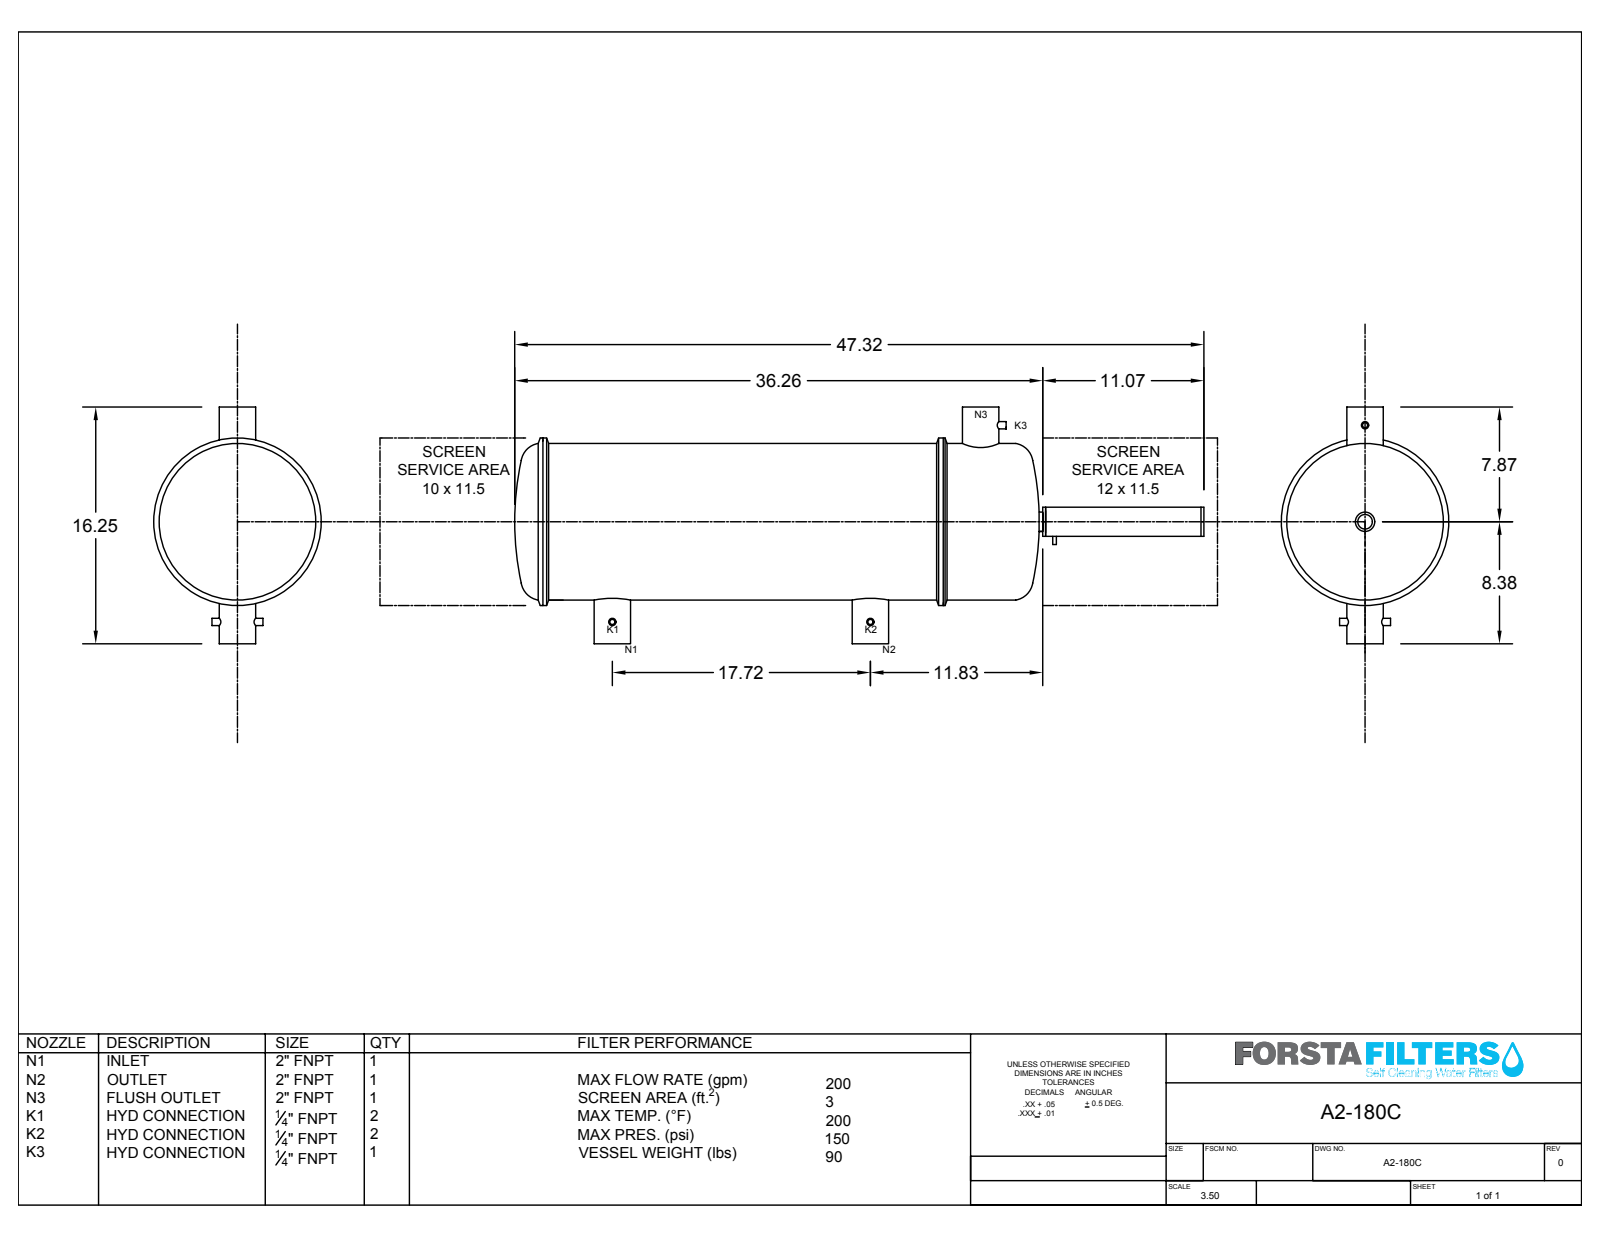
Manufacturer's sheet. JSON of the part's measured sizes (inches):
{"part_name": "A2-180C", "step_written_by": "SolidWorks 2017 (CONFIG_CONTROL_DESIGN)", "units": "inches", "bodies": {"solids": 6, "faces": 141, "planar": 39, "cylindrical": 58, "other": 44}, "overall_size": [47.324, 16.25, 11.493], "volume_in3": 311, "surface_area_in2": 2969, "round_holes": [[0.25, 3], [2, 3], [1, 2], [0.093, 1], [0.936, 1], [10.35, 1]], "round_bosses_or_shafts": [[2.394, 3], [0.644, 3], [11.493, 1], [10.743, 1], [1.993, 1], [0.25, 1]], "partial_cylinders_radius": [[1, 2]], "face_to_face_distances": [0.25, 0.2, 10.867, 45.187, 34.519, 10.667, 45.387, 34.319, 11.067, 16.25], "hole_center_spacings": [13.8, 5.041, 6.691, 11.881, 13.755, 13.968, 16, 16.922]}
